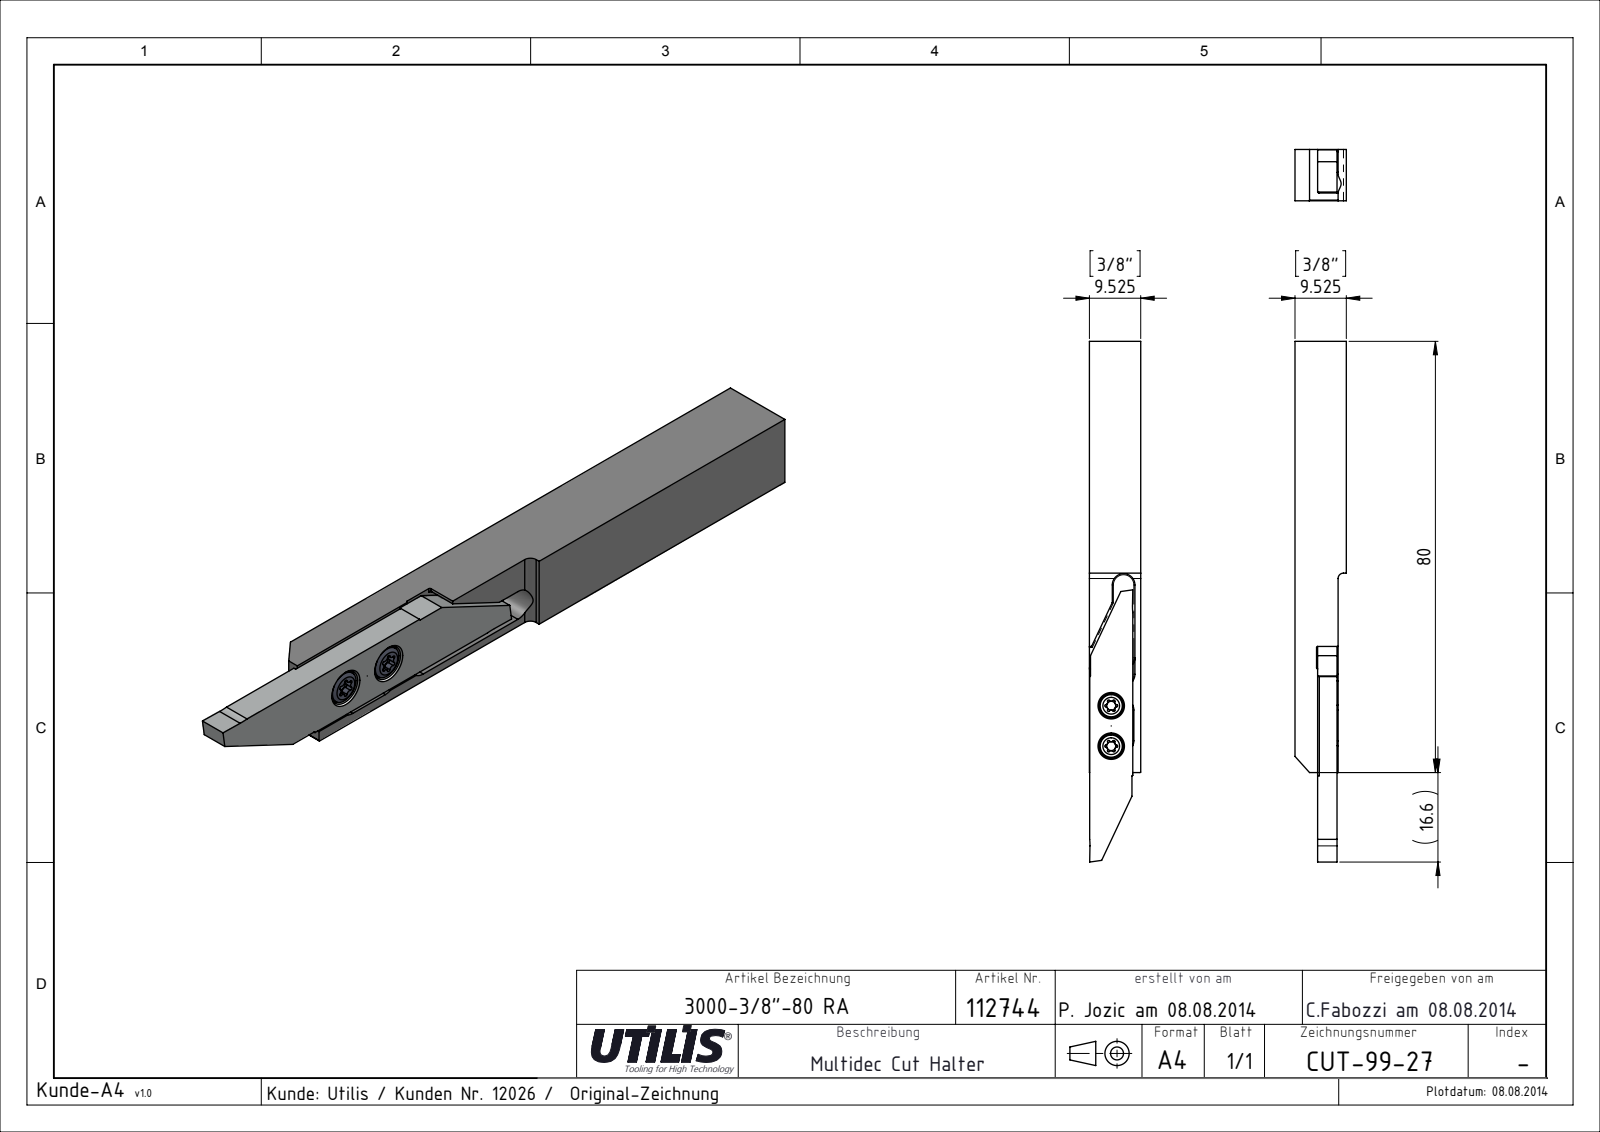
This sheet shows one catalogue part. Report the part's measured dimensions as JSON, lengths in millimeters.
{"part_name": "MSP-16_M3x7.3 T08; CUT- 3000 R+L Lang NUR FÜR KUNDEN _L-Lang; CUT-99-27; CUT-99-Kunde_3000-3-8-80 RA", "step_written_by": "SolidWorks 2014 (CONFIG_CONTROL_DESIGN)", "units": "millimeters", "bodies": {"solids": 4, "faces": 119, "planar": 35, "cylindrical": 56, "other": 28}, "overall_size": [96.6, 9.53, 9.53], "volume_mm3": 6800, "surface_area_mm2": 4498, "round_holes": [[2.5, 2], [4.9, 2]], "round_bosses_or_shafts": [[4.1, 2], [3, 2]], "partial_cylinders_radius": [[0.2, 12], [0.45, 12], [2.1, 4], [10, 2], [1, 1]], "face_to_face_distances": [9.52, 4.2, 5.32, 7.8, 3.6, 1.72, 8, 1.47, 8.05, 9.47], "hole_center_spacings": [3.75, 7.5, 3.65, 3.85, 7.4, 7.6]}
